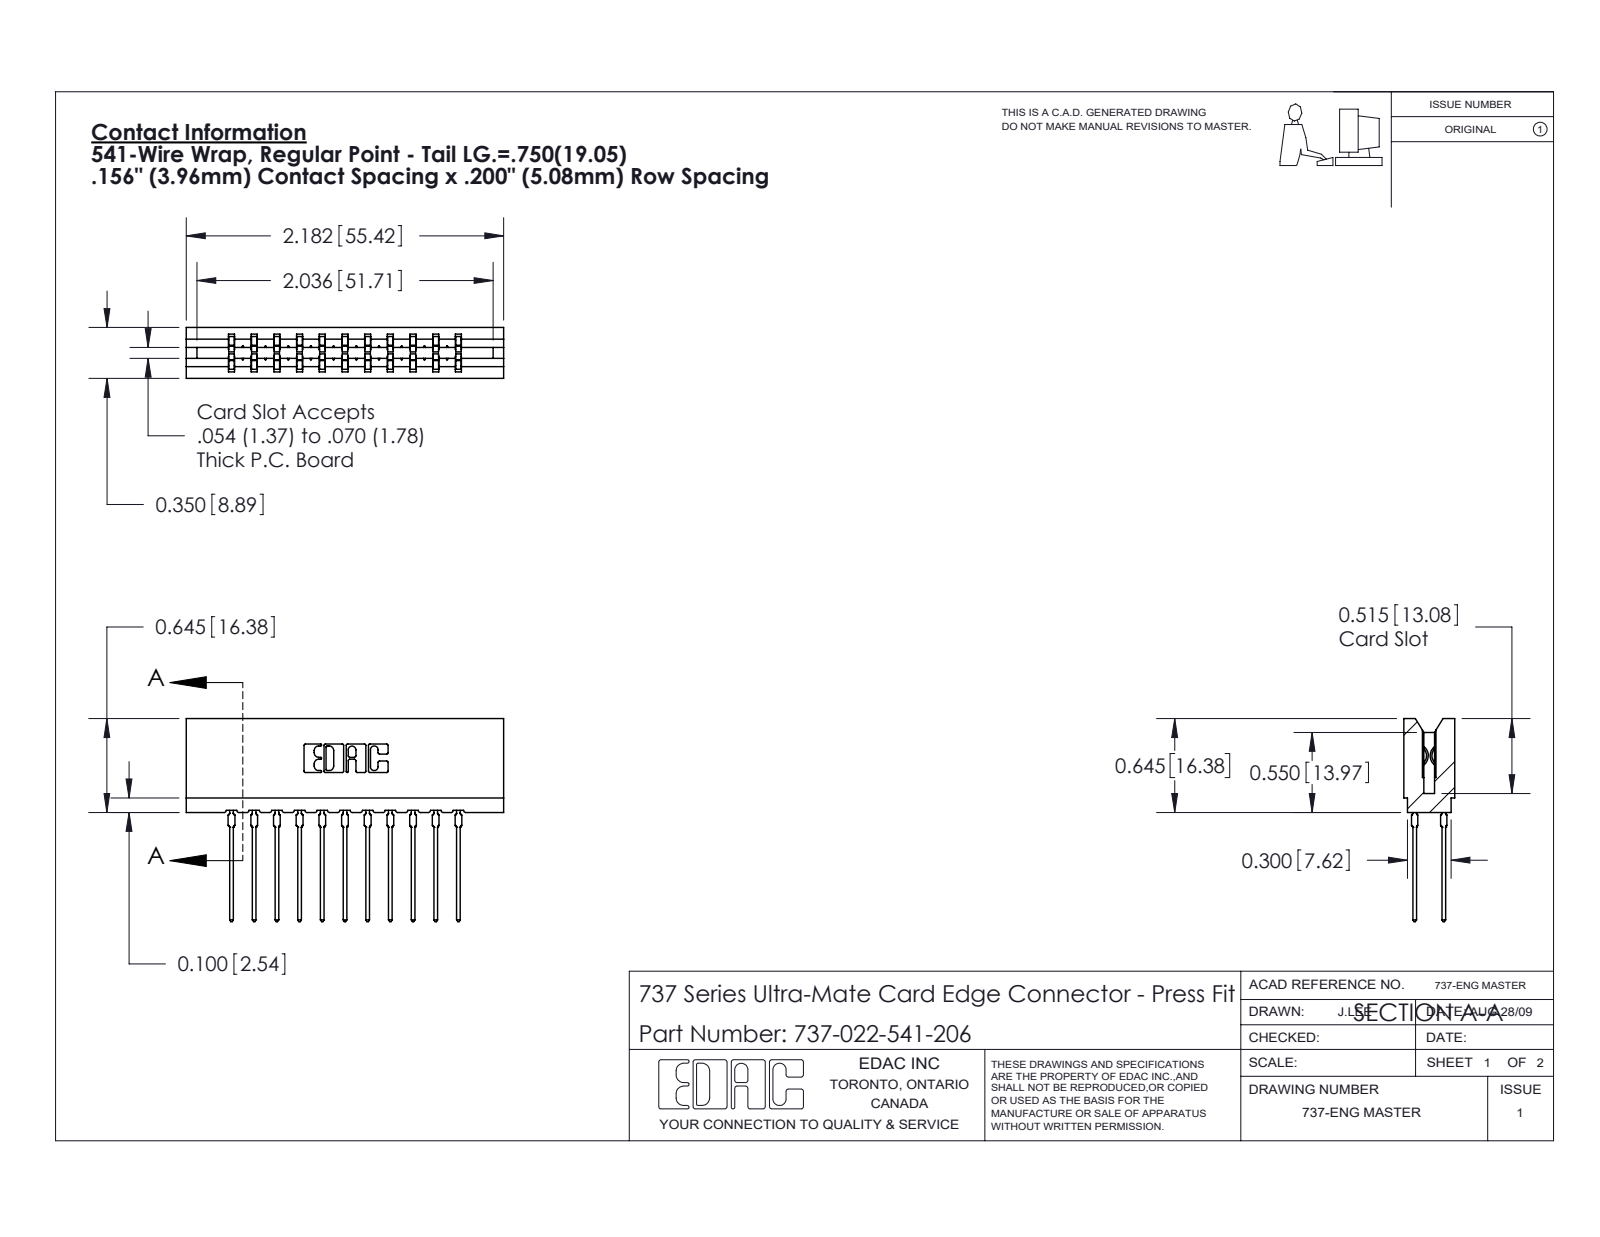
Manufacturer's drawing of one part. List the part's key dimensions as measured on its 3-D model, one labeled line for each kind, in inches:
Part name (STEP PRODUCT): 745-292-001_541; 737-022-541-206; 737 Part_Insulator Option - 06
STEP written by: SolidWorks 2020 (CONFIG_CONTROL_DESIGN)
Units: inches
Bodies: 23 solids, 2075 faces (1078 planar, 425 cylindrical, 572 other)
Overall size (bounding box): 2.182 × 1.396 × 0.35
Volume: 0.352 in³ · Surface area: 12.69 in²
Partial cylindrical surfaces — rounded edges, fillets, slot ends (radius × count): R0.021 ×44, R0.01 ×22, R0.015 ×22, R0.005 ×8, R0.011 ×8, R0.007 ×6, R0.031 ×6, R0.026 ×3
Main face-to-face distances: 0.156, 0.138, 0.212, 0.35, 0.624, 0.063, 0.287, 0.076, 0.149, 0.354
